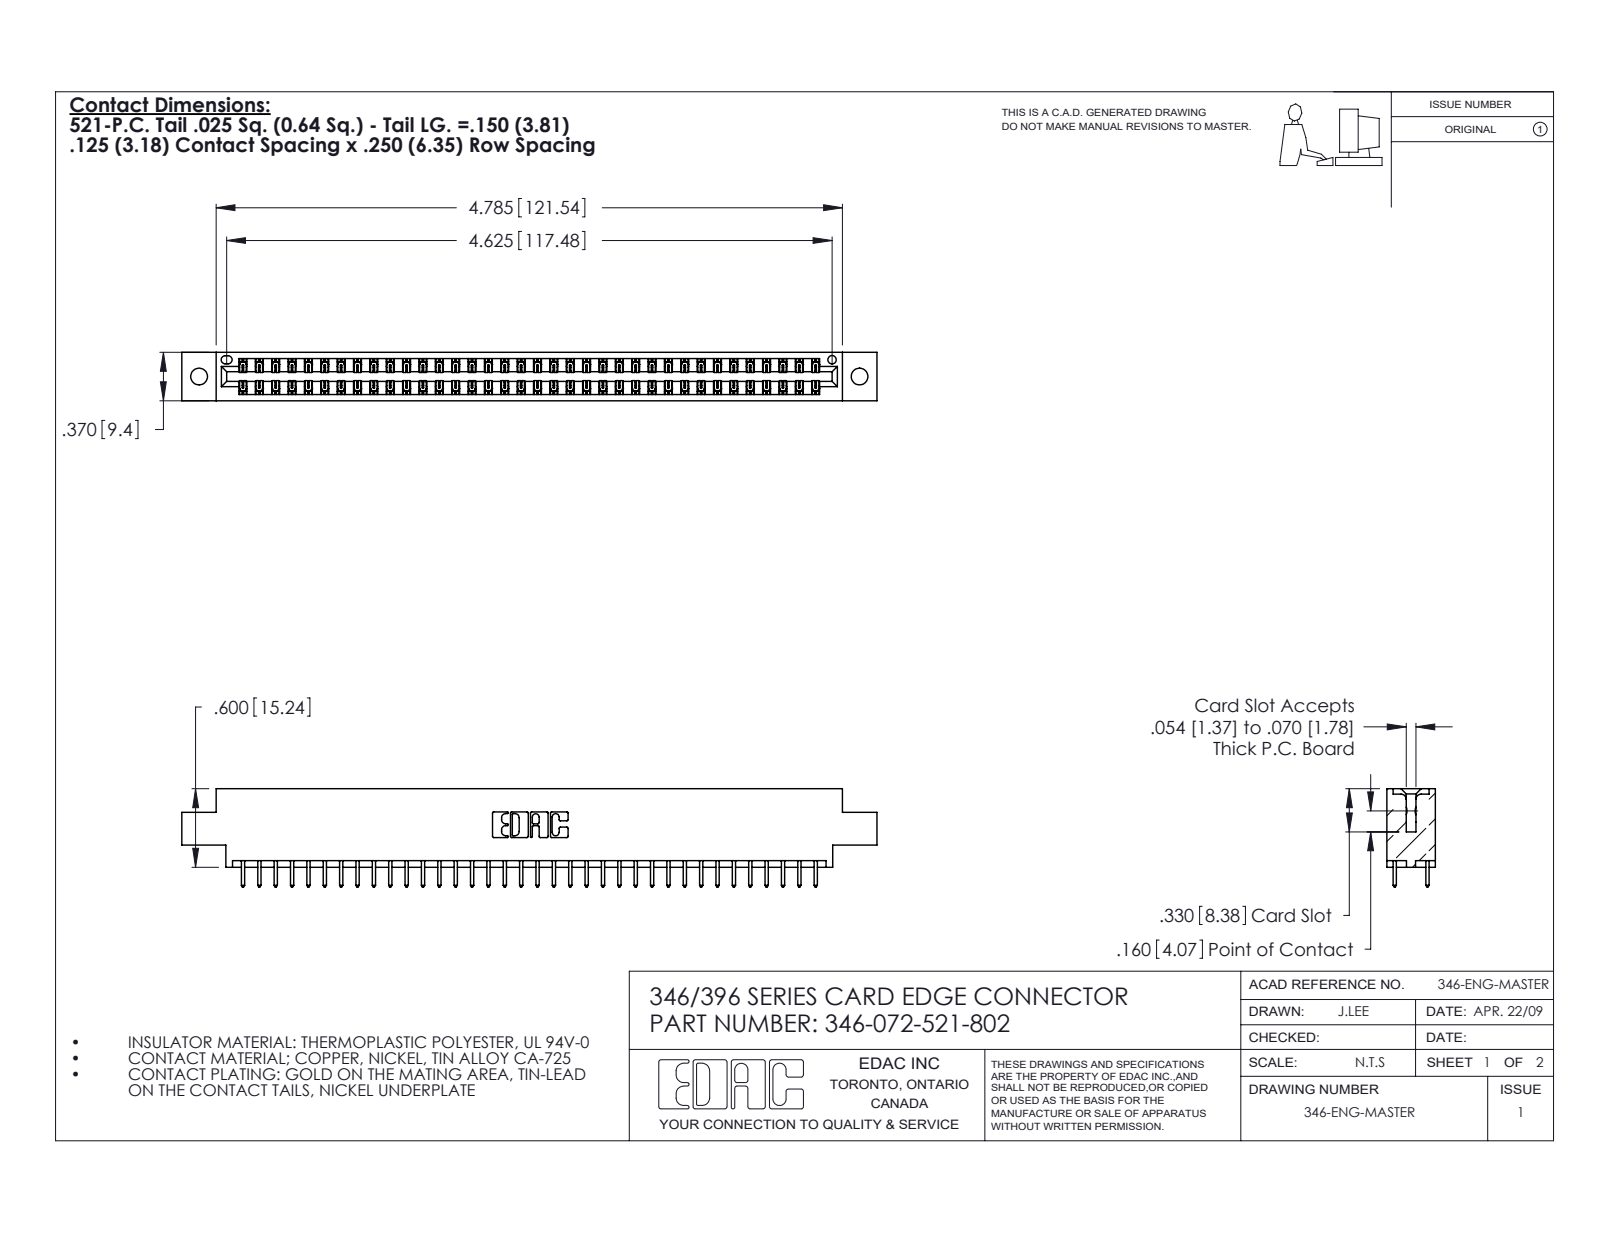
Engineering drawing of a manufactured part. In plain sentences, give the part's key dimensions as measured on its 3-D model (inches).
The part is named "346-072-521-802; 345-292-001_345-293-121; 346 Part_0.170 Offset - 0.128 Dia". Its 3-D file was written by "SolidWorks 2020 (CONFIG_CONTROL_DESIGN)". It is 73 solids with 3870 faces: 2600 planar, 1270 cylindrical and 0 other. Overall it measures 5.31 by 0.75 by 0.37 inches. Its volume is 0.786 cubic inches and its surface area 26.86 square inches. Round holes: 2 of diameter 0.128, 1 of diameter 0.064. Partial cylindrical surfaces (rounded edges, fillets, slot ends): 108 of radius 0.006, 72 of radius 0.01, 22 of radius 0.01, 6 of radius 0.007, 6 of radius 0.031, 3 of radius 0.026, 2 of radius 0.014, 2 of radius 0.022. The main face-to-face distances are 0.048, 0.322, 0.37, 0.25, 0.072, 0.298, 0.025, 0.275, 0.148, 0.222. The hole center spacings are 0.246, 4.836, 5.045.
